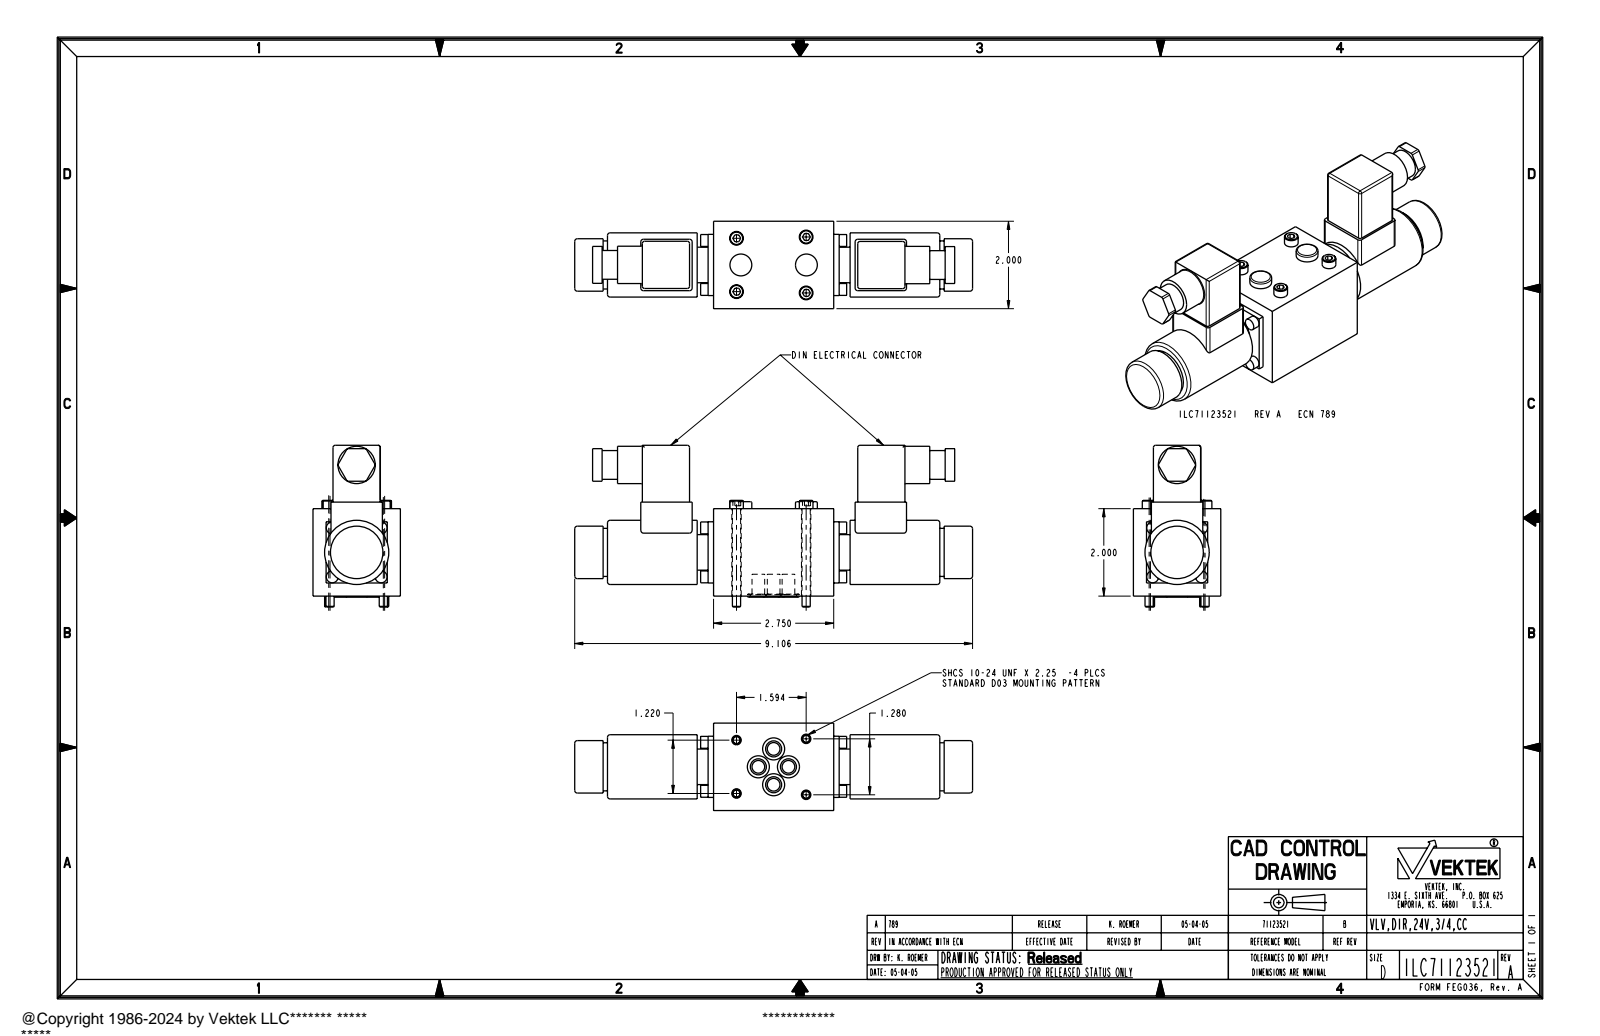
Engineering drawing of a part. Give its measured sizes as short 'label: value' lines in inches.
name: ILC71123521
written by: PRO/ENGINEER BY PARAMETRIC TECHNOLOGY CORPORATION, 2004290 (AUTOMOTIVE_DESIGN_CC2)
unit: in
bodies: 1 solid, 282 faces (120 planar, 118 cylindrical, 44 other)
size: 9.106 × 3.7 × 2
volume: 25.88 in³; area: 100.3 in²
holes: 4× ⌀0.215, 4× ⌀0.29, 4× ⌀0.49
bosses: 4× ⌀0.313, 4× ⌀0.272, 4× ⌀0.187, 2× ⌀0.854, 2× ⌀0.658, 2× ⌀0.5, 1× ⌀1.469, 1× ⌀1.2
rounds: 26× R0.05, 8× R0.06
face distances: 2, 1.08, 0.412, 1.588, 0.55, 0.125, 0.458, 0.462, 1.538, 1.542
hole spacings: 0.532, 0.539, 0.757, 0.779, 0.789, 0.873, 1.268, 1.287
